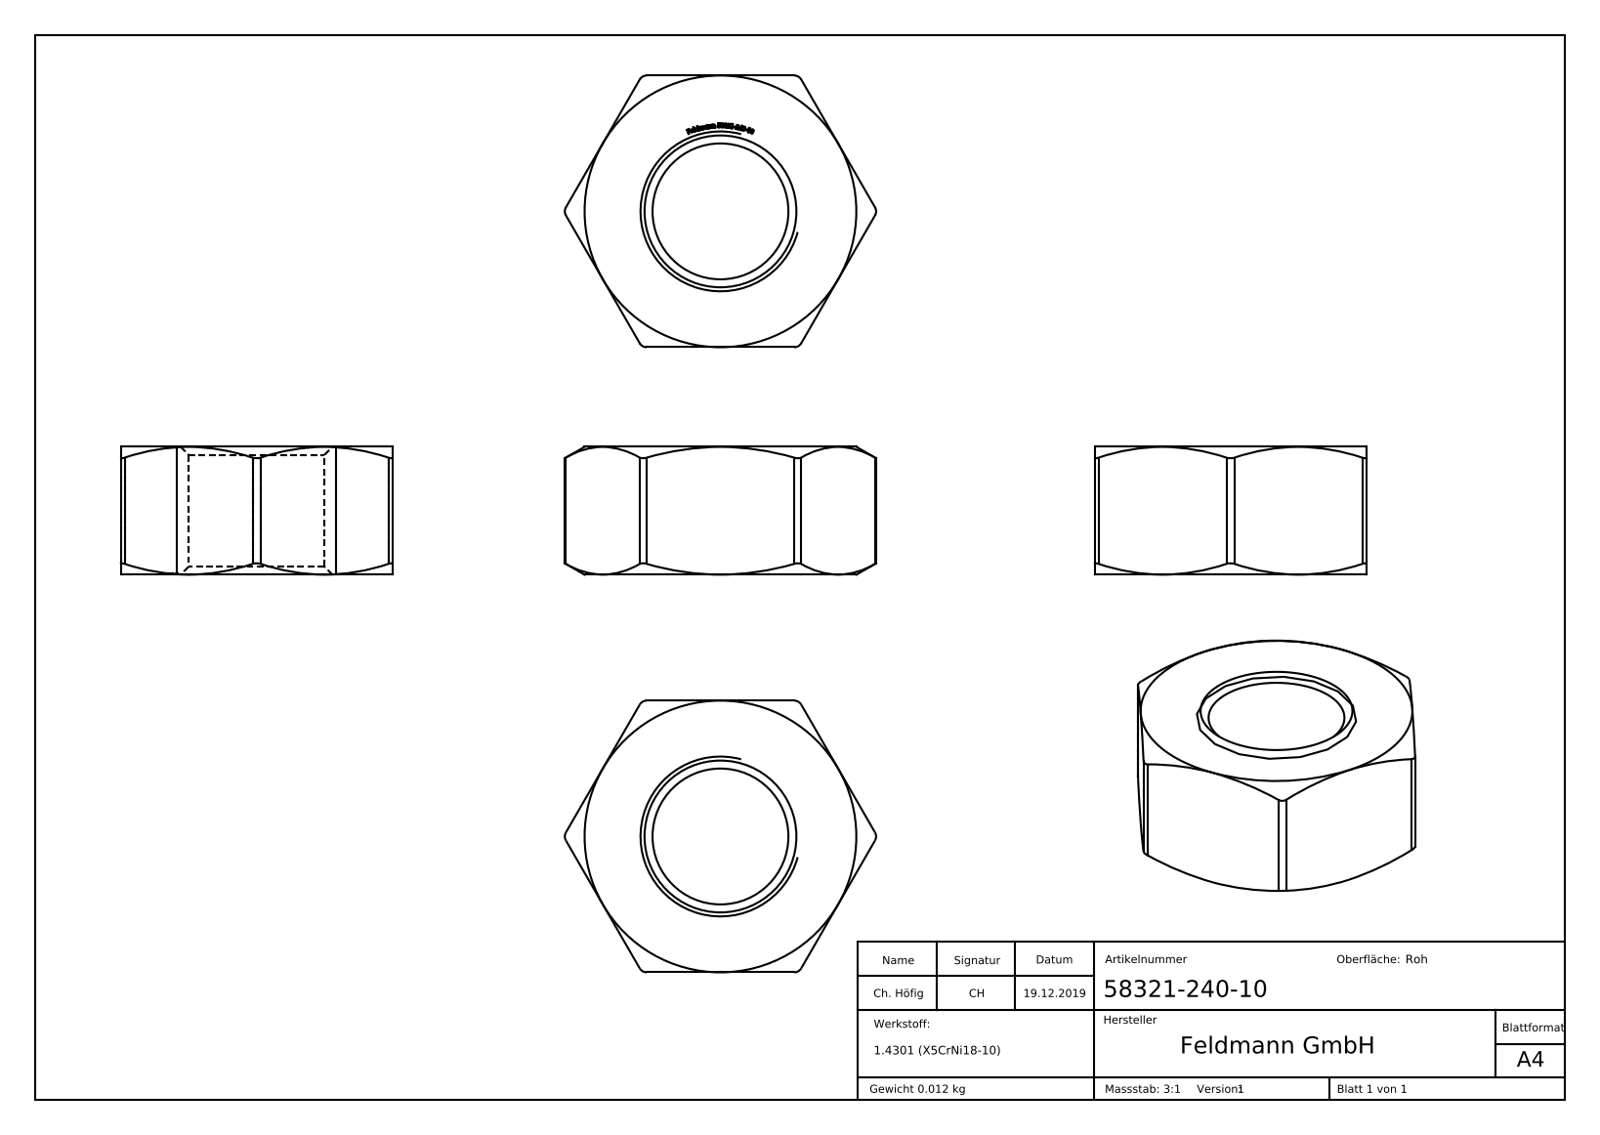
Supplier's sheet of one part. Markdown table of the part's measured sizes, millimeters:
| quantity | value |
| --- | --- |
| part name | 58321-240-10 |
| STEP written by | SolidWorks 2015 (CONFIG_CONTROL_DESIGN) |
| units | millimeters |
| bodies | 1 solid, 282 faces (144 planar, 7 cylindrical, 131 other) |
| overall size | 22 × 19.48 × 17 |
| volume | 1 530 mm³ |
| surface area | 1 033 mm² |
| round holes (diameter × count) | 8.5 × 1 |
| partial cylindrical surfaces (radius × count) | 0.5 × 6 |
| main face-to-face distances | 17, 8, 7.9, 1.01, 1.1 |
